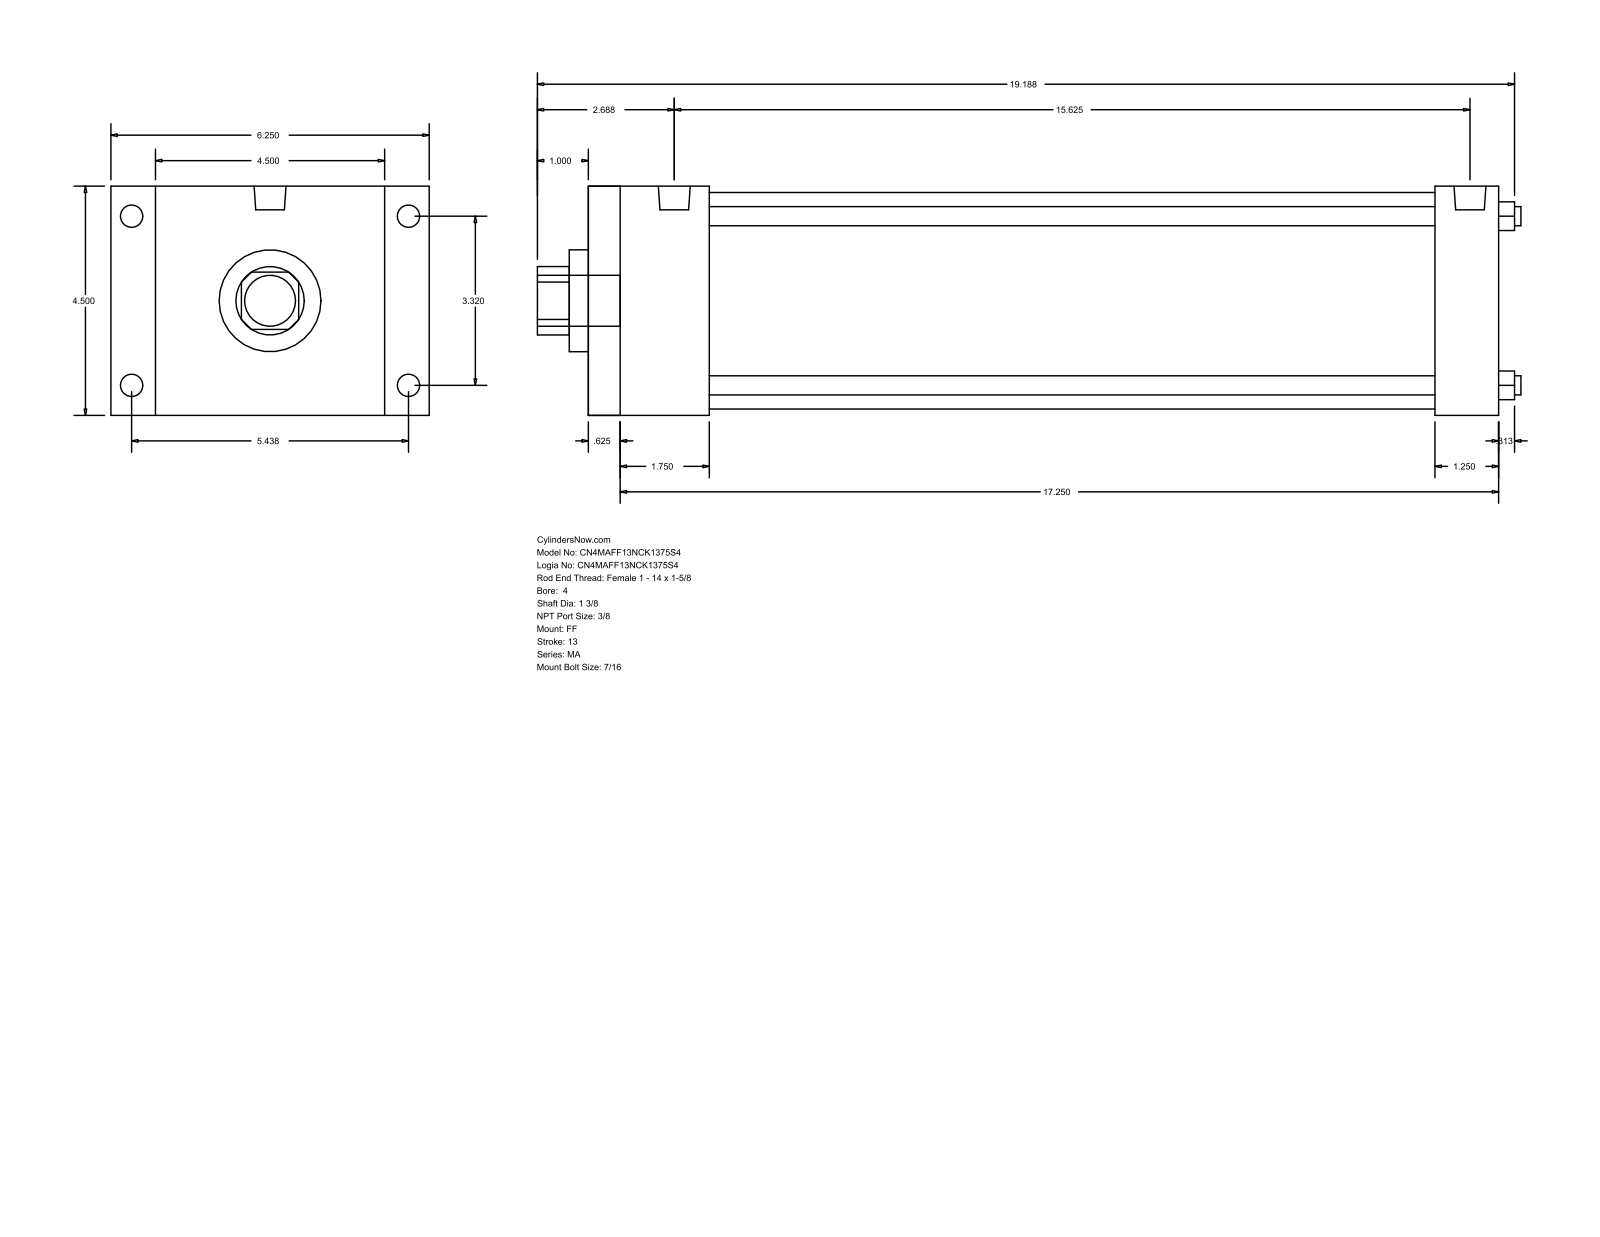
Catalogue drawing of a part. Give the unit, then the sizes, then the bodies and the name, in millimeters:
Units: millimetres
Overall size (bounding box): 490.54 × 158.75 × 114.3
Round holes (diameter × count): ⌀9.53 ×4, ⌀34.92 ×1, ⌀50.8 ×1, ⌀107.95 ×1
Round bosses / shafts (diameter × count): ⌀11.11 ×8, ⌀15.93 ×2, ⌀25.4 ×1
Partial cylindrical surfaces — rounded edges, fillets, slot ends (radius × count): R17.06 ×1
Main face-to-face distances: 114.3, 454.03, 15.87, 438.16, 22.23, 136.53, 422.28, 406.41, 31.75, 60.32
Hole centre spacings: 59.62, 84.32, 119.25
Bodies: 0 solids, 92 faces (64 planar, 28 cylindrical, 0 other)
Part name (STEP PRODUCT): MA_FF__0400_1.375
STEP written by: GSSL Pune (CONFIG_CONTROL_DESIGN)
